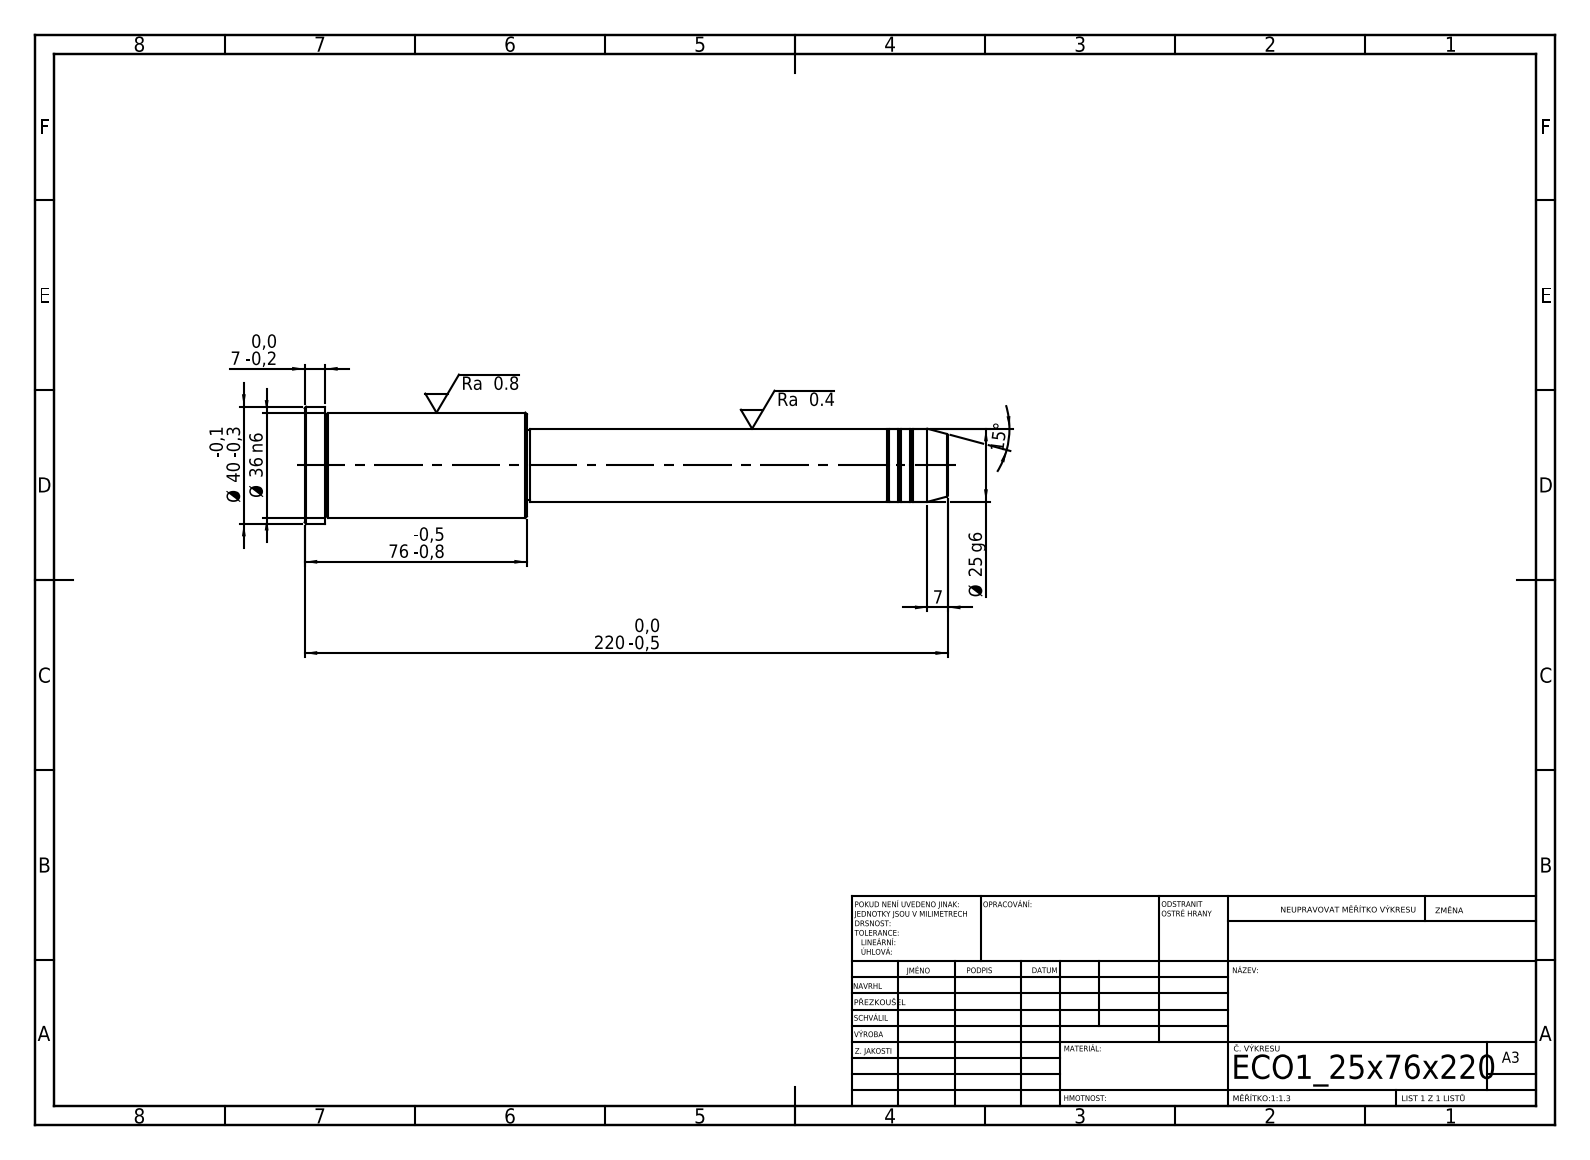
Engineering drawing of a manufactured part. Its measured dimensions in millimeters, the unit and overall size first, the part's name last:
Units: millimetres
Overall size (bounding box): 220 × 40 × 40
Round bosses / shafts (diameter × count): ⌀40 ×1, ⌀36 ×1, ⌀25 ×1, ⌀24 ×1
Main face-to-face distances: 76, 144, 220, 213, 69, 7, 143, 1, 70, 77
Volume: 149 021 mm³ · Surface area: 22 529 mm²
Bodies: 1 solid, 43 faces (5 planar, 14 cylindrical, 24 other)
STEP written by: SolidWorks 2019 (CONFIG_CONTROL_DESIGN)
